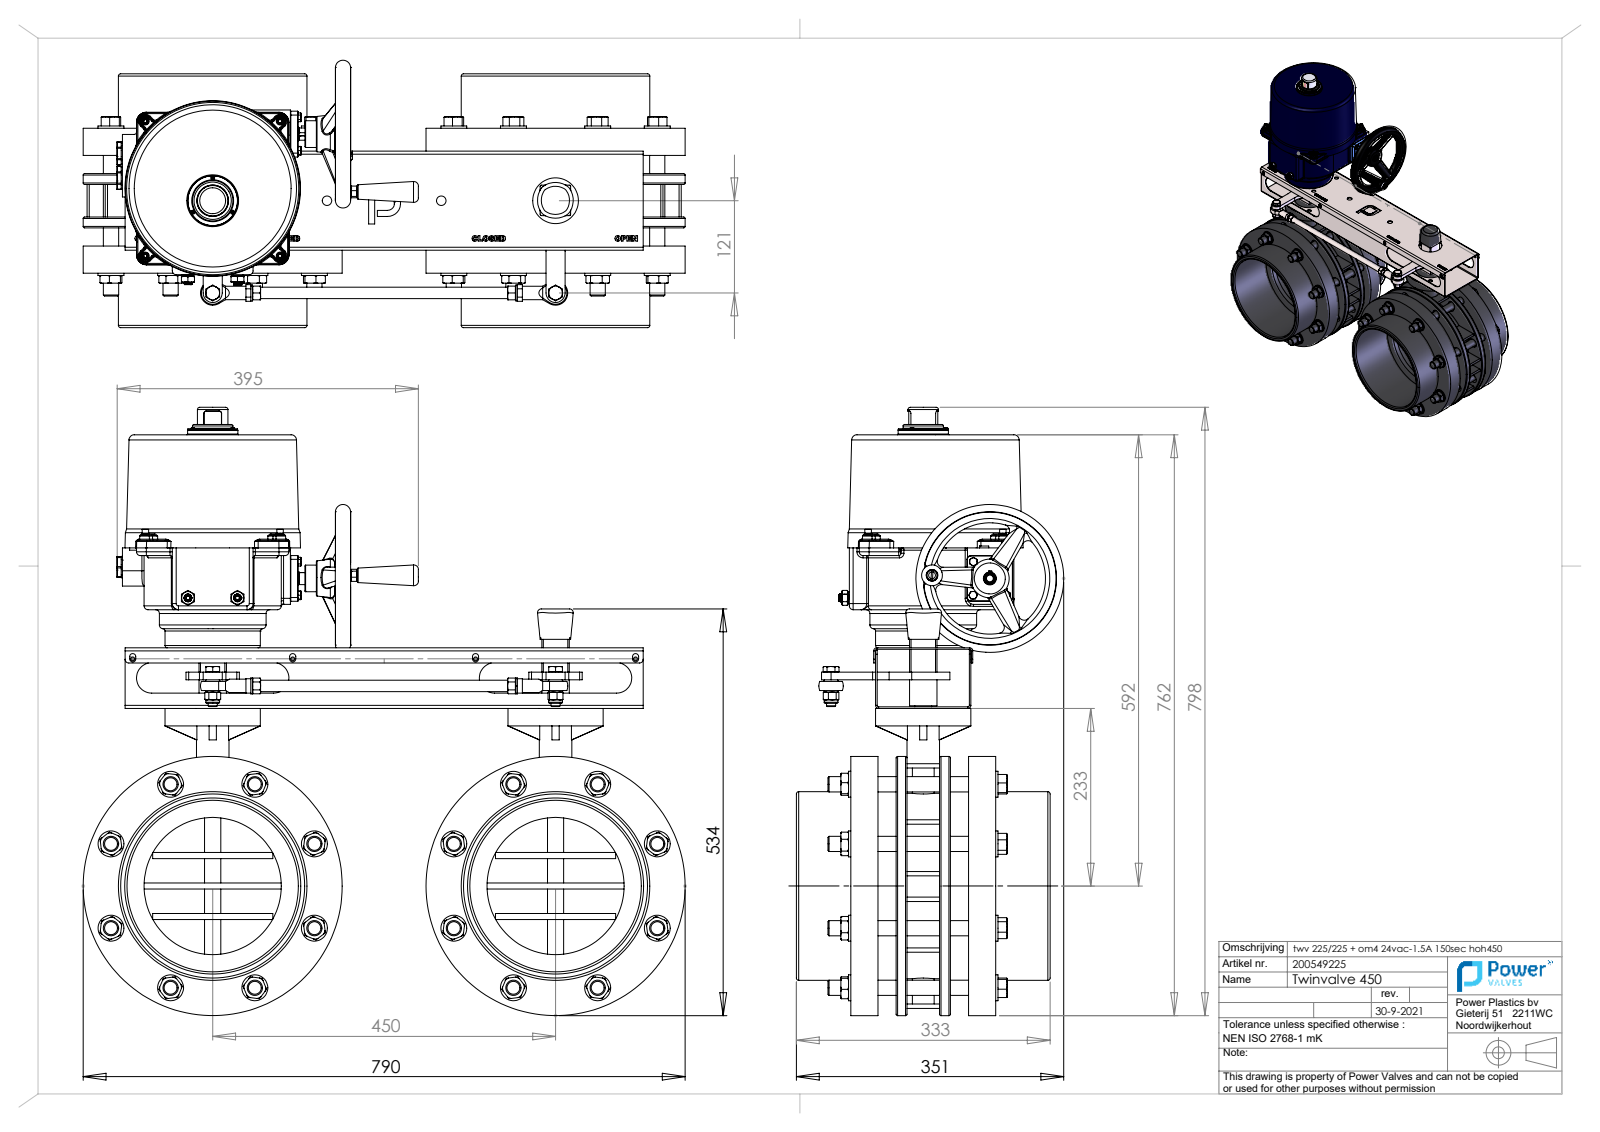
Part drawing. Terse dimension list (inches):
name: 200.549.225 twv 225 450 VDL
written by: SolidWorks 2018 (AUTOMOTIVE_DESIGN)
unit: in
bodies: 0 solids, 2111 faces (762 planar, 756 cylindrical, 593 other)
size: 31.417 × 31.102 × 13.815
holes: 12× ⌀0.413, 8× ⌀0.433, 7× ⌀0.197, 4× ⌀0.33, 2× ⌀0.492, 2× ⌀0.54, 2× ⌀2.953, 2× ⌀7.087, 2× ⌀7.874, 2× ⌀8.858, 1× ⌀0.315, 1× ⌀0.591
bosses: 16× ⌀1.339, 16× ⌀0.787, 4× ⌀0.394, 4× ⌀0.335, 4× ⌀0.315, 3× ⌀0.709, 3× ⌀0.591, 2× ⌀13.386
rounds: 34× R0.118, 32× R0.453, 24× R0.113, 19× R0.197, 18× R0.059, 9× R0.157, 7× R0.512, 6× R0.787
face distances: 0.079, 3.74, 0.937, 3.051, 1.406, 2.343, 5.146, 6.083, 2.904, 4.585
hole spacings: 17.717, 2.008, 2.839, 0.933, 2.851, 3.203, 3.633, 3.75
